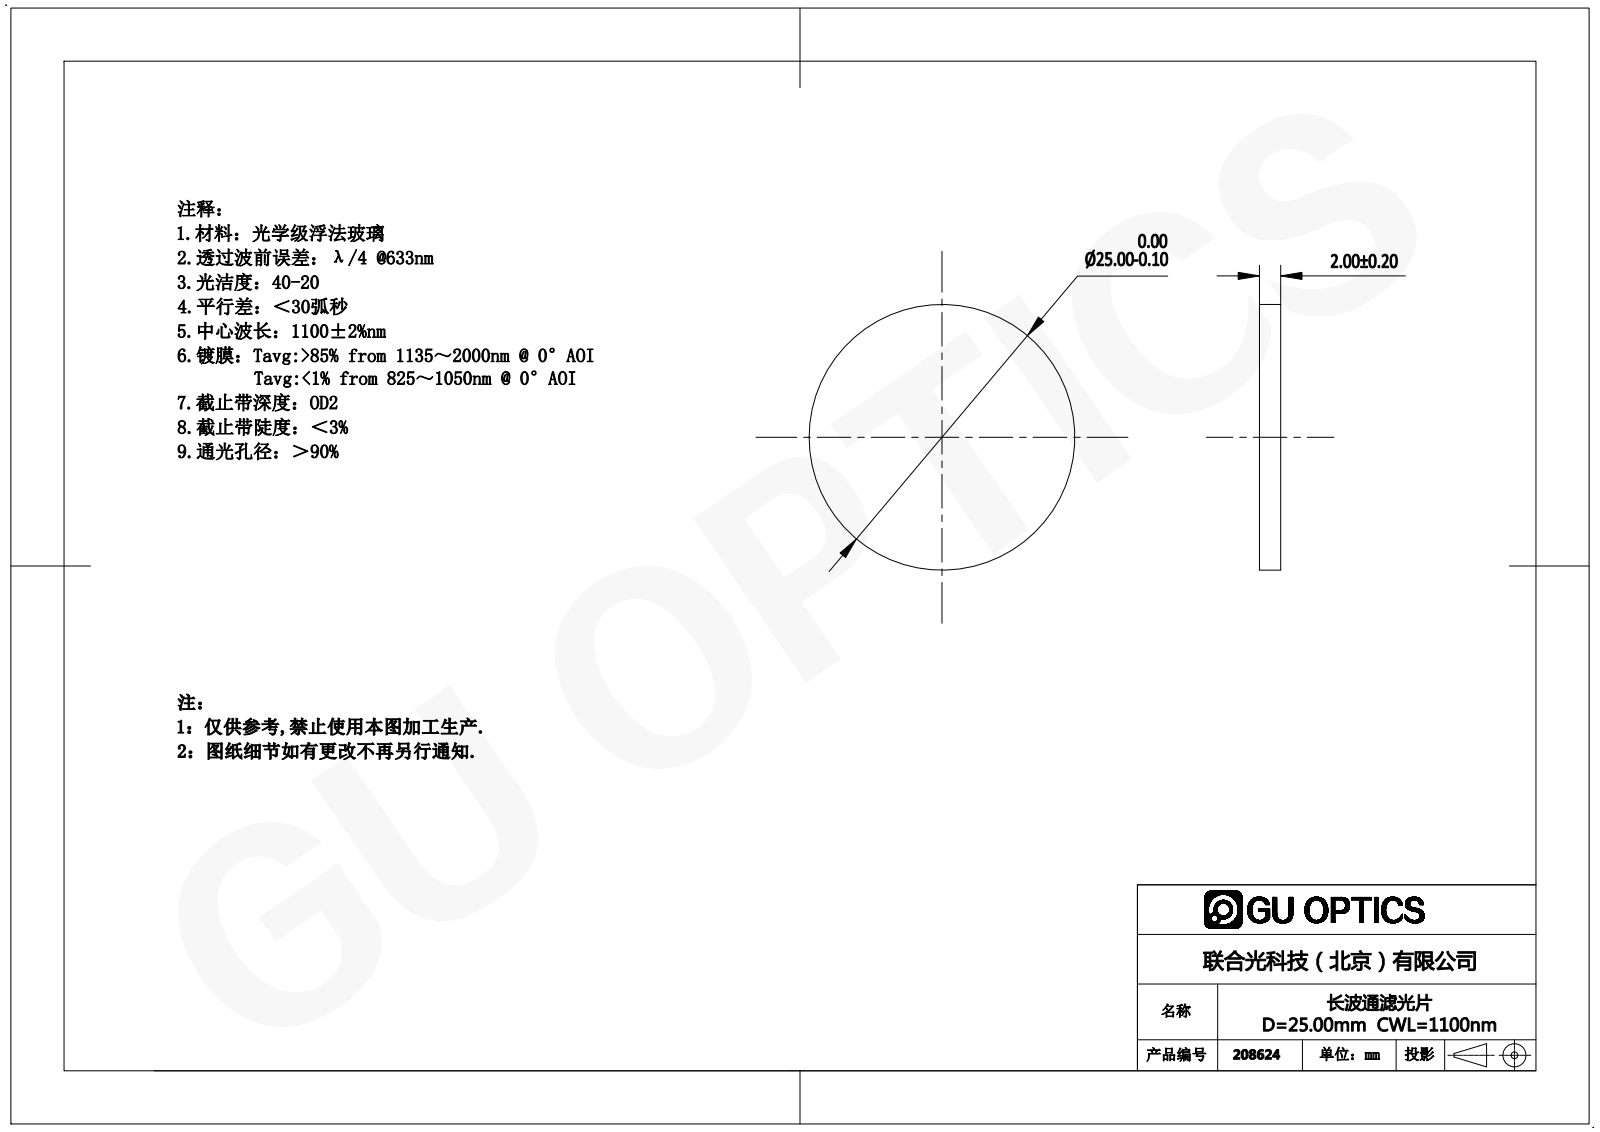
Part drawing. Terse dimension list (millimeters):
name: 208610
written by: SolidWorks 2016 (AUTOMOTIVE_DESIGN)
unit: mm
bodies: 1 solid, 4 faces (2 planar, 2 cylindrical, 0 other)
size: 25 × 25 × 2
volume: 982 mm³; area: 1 139 mm²
bosses: 1× ⌀25
face distances: 2
